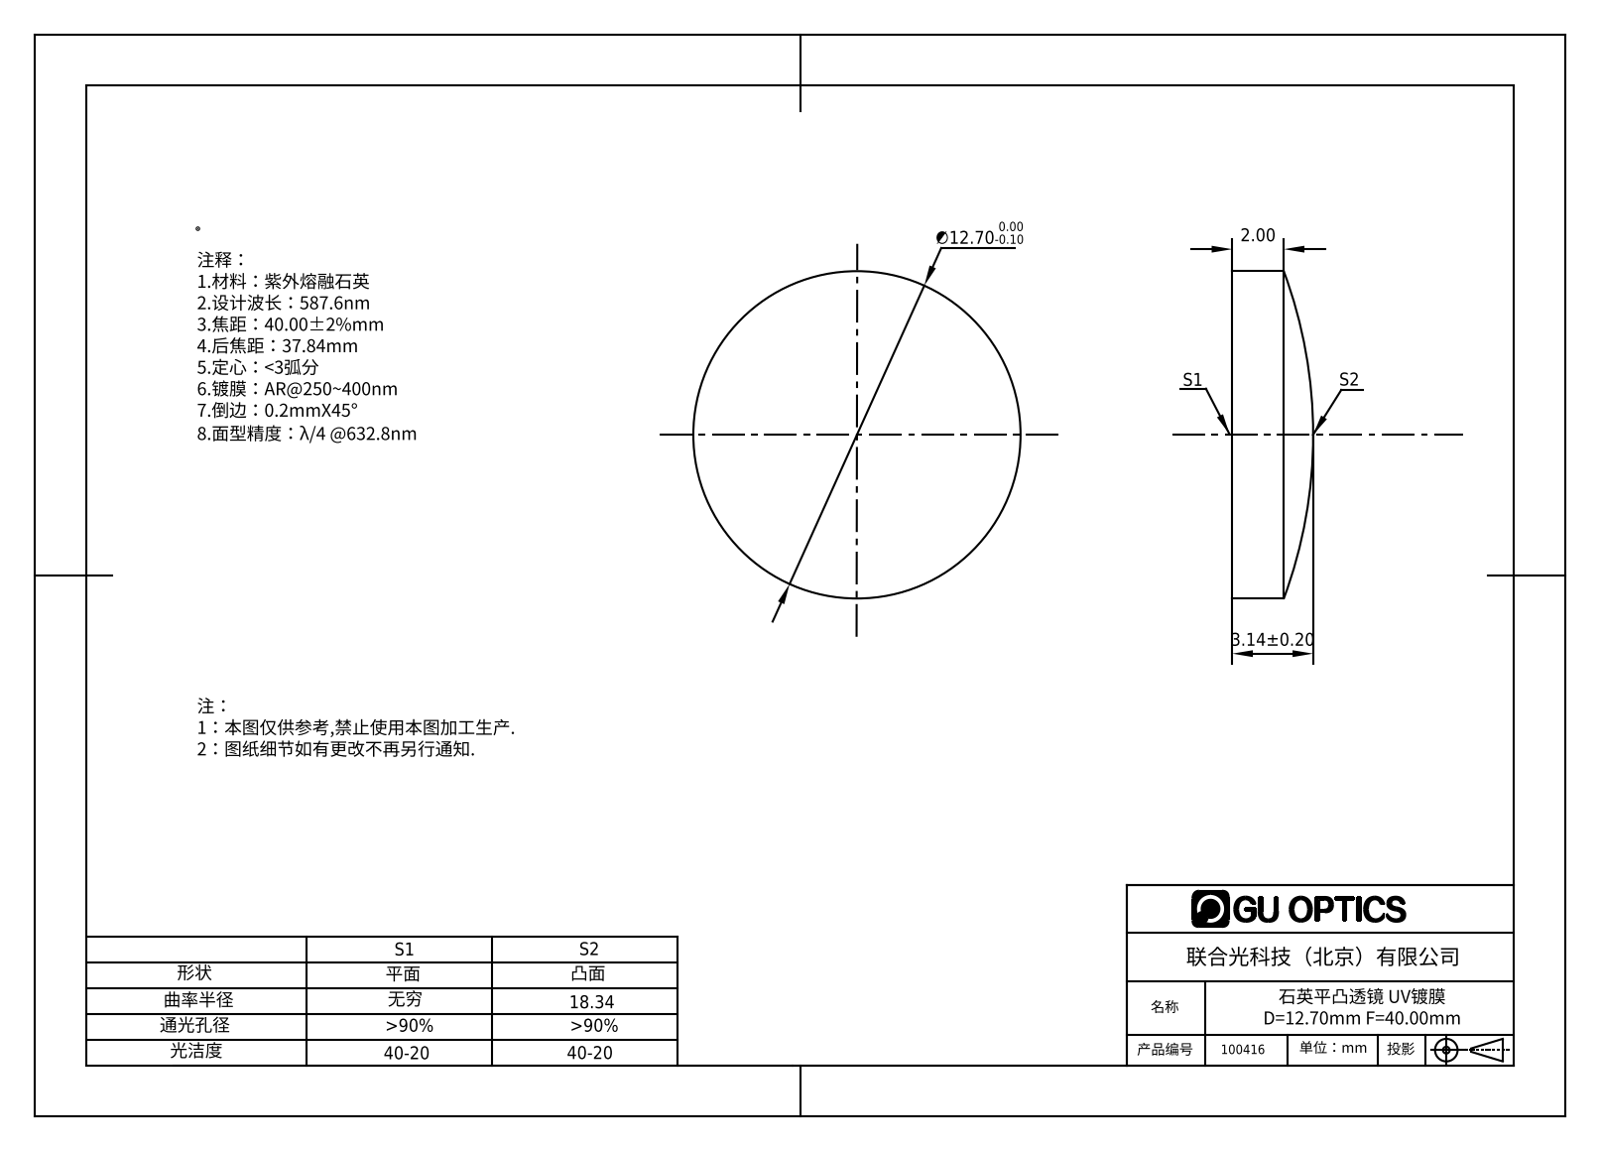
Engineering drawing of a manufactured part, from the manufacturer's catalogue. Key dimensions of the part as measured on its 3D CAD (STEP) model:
Part name (STEP PRODUCT): 100366
STEP written by: SolidWorks 2016 (AUTOMOTIVE_DESIGN)
Units: millimetres
Bodies: 1 solid, 5 faces (1 planar, 2 cylindrical, 2 other)
Overall size (bounding box): 12.7 × 12.7 × 3.14
Volume: 326 mm³ · Surface area: 337 mm²
Round bosses / shafts (diameter × count): ⌀12.7 ×1
